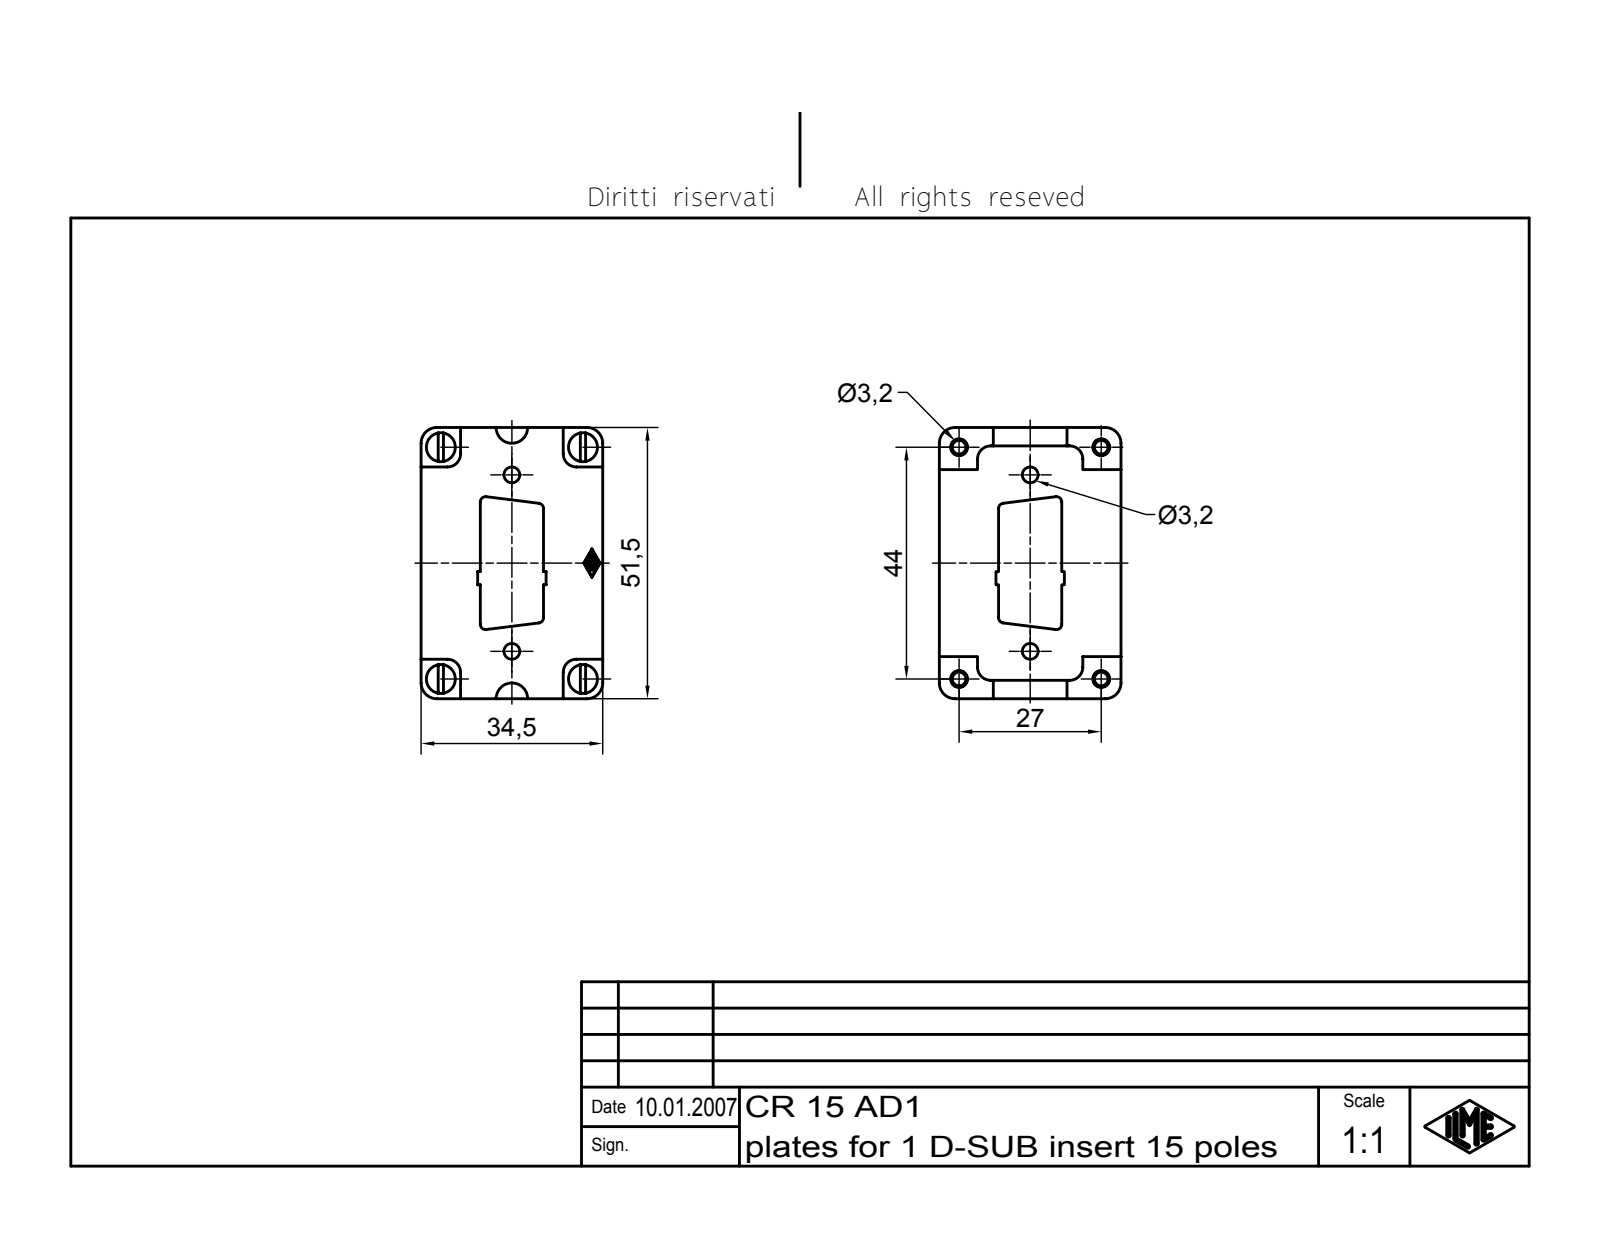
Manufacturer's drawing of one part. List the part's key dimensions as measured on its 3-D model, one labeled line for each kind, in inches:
Part name (STEP PRODUCT): CR 15 AD1
STEP written by: Autodesk Inventor 7 (AUTOMOTIVE_DESIGN)
Units: inches
Bodies: 1 solid, 195 faces (117 planar, 62 cylindrical, 16 other)
Overall size (bounding box): 2.028 × 1.358 × 0.551
Volume: 0.401 in³ · Surface area: 9.037 in²
Round holes (diameter × count): ⌀0.126 ×4, ⌀0.118 ×2
Round bosses / shafts (diameter × count): ⌀0.217 ×4, ⌀0.118 ×4
Partial cylindrical surfaces — rounded edges, fillets, slot ends (radius × count): R0.004 ×14, R0.098 ×8, R0.118 ×6, R0.039 ×4
Main face-to-face distances: 0.118, 0.315, 0.276, 0.079, 0.394, 2.028, 0.039, 1.713, 1.358, 0.138
Hole centre spacings: 0.57, 0.57, 1.063, 1.615, 1.616, 1.732, 2.032, 1.319
